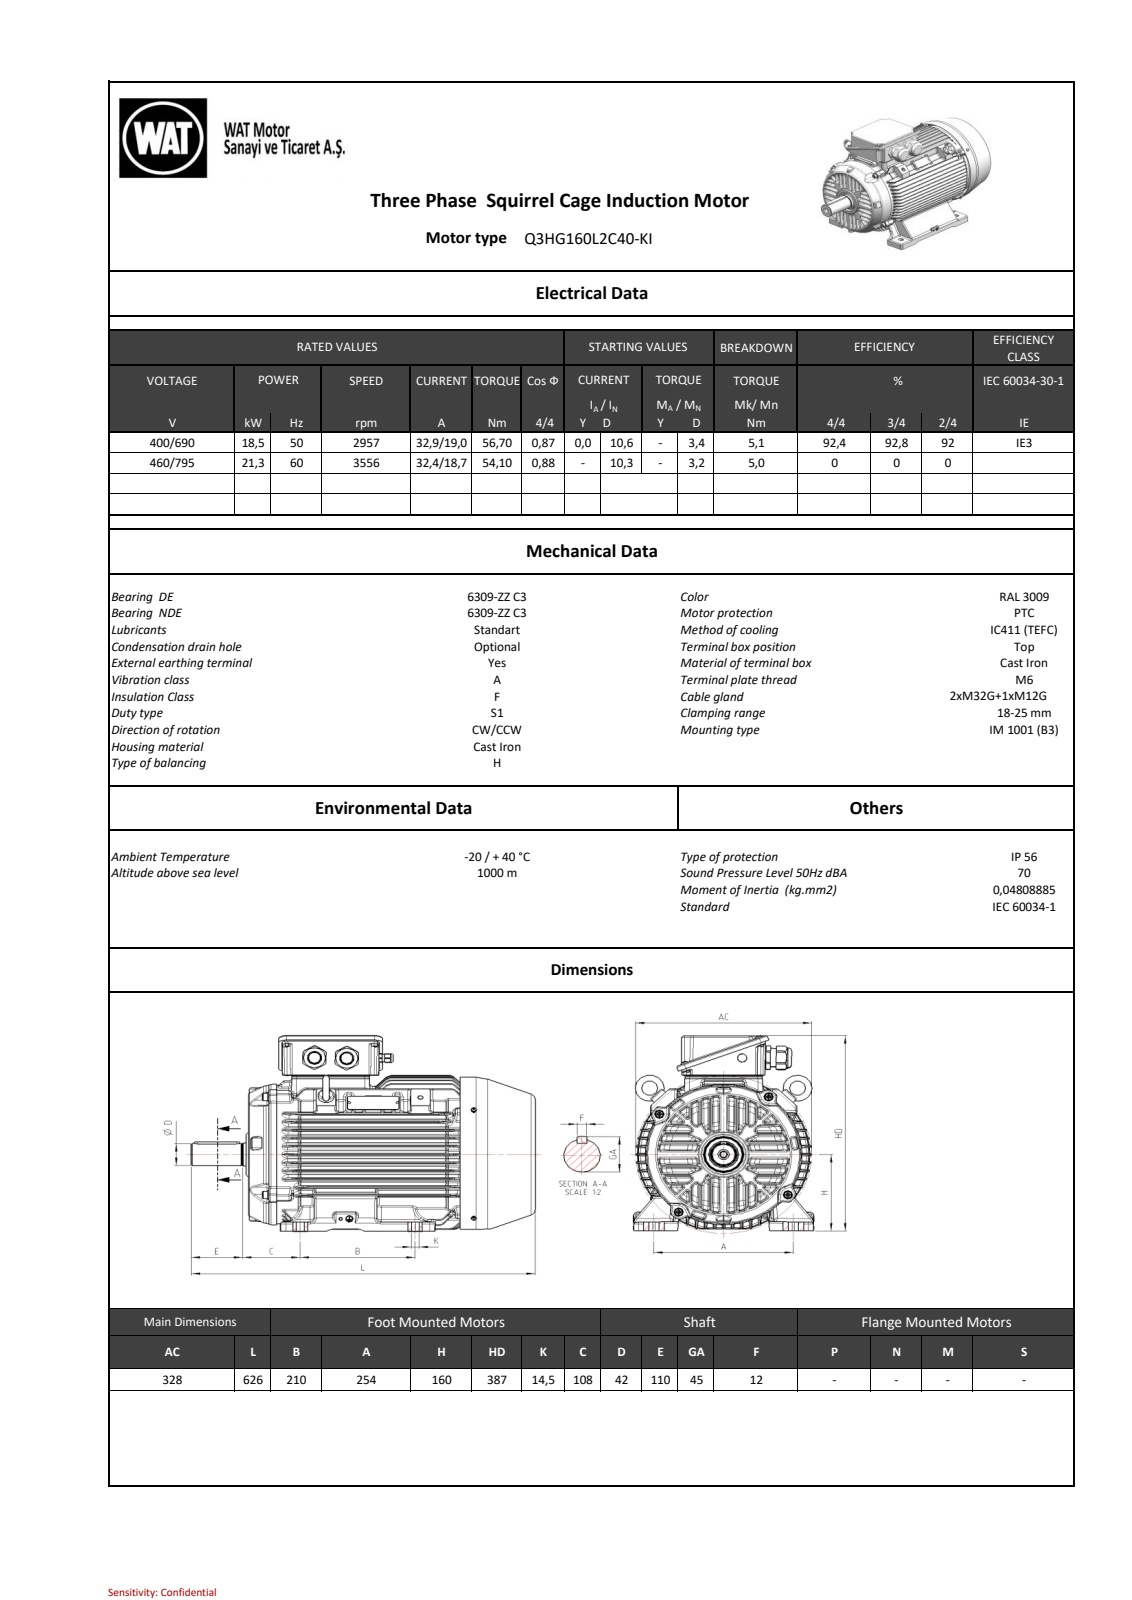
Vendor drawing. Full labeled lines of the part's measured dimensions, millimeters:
Part name (STEP PRODUCT): C9017F38B806svt2
STEP written by: SIEMENS PLM Software NX 11.0 (AUTOMOTIVE_DESIGN)
Units: millimetres
Bodies: 0 solids, 6282 faces (1236 planar, 1829 cylindrical, 3217 other)
Overall size (bounding box): 625.5 × 388.3 × 327.37
Round holes (diameter × count): ⌀5.5 ×8, ⌀9 ×6, ⌀4.2 ×5, ⌀5.3 ×4, ⌀2.5 ×2, ⌀10.9 ×2, ⌀19 ×2, ⌀21 ×2, ⌀5.2 ×1, ⌀10 ×1, ⌀14 ×1, ⌀17 ×1
Round bosses / shafts (diameter × count): ⌀16 ×8, ⌀20 ×4, ⌀10 ×3, ⌀34.5 ×2, ⌀31.25 ×2, ⌀30 ×2, ⌀317 ×1, ⌀282 ×1
Partial cylindrical surfaces — rounded edges, fillets, slot ends (radius × count): R5 ×213, R3 ×186, R4 ×149, R1.5 ×120, R2 ×65, R1.8 ×58, R3.5 ×45, R0.4 ×34
Main face-to-face distances: 137.45, 15.17, 30.42, 15.25, 122.2, 45.73, 106.89, 30.56, 15.31, 107.03
Hole centre spacings: 136, 144, 123.21, 123.22, 183.51, 183.52, 203.65, 165.2
